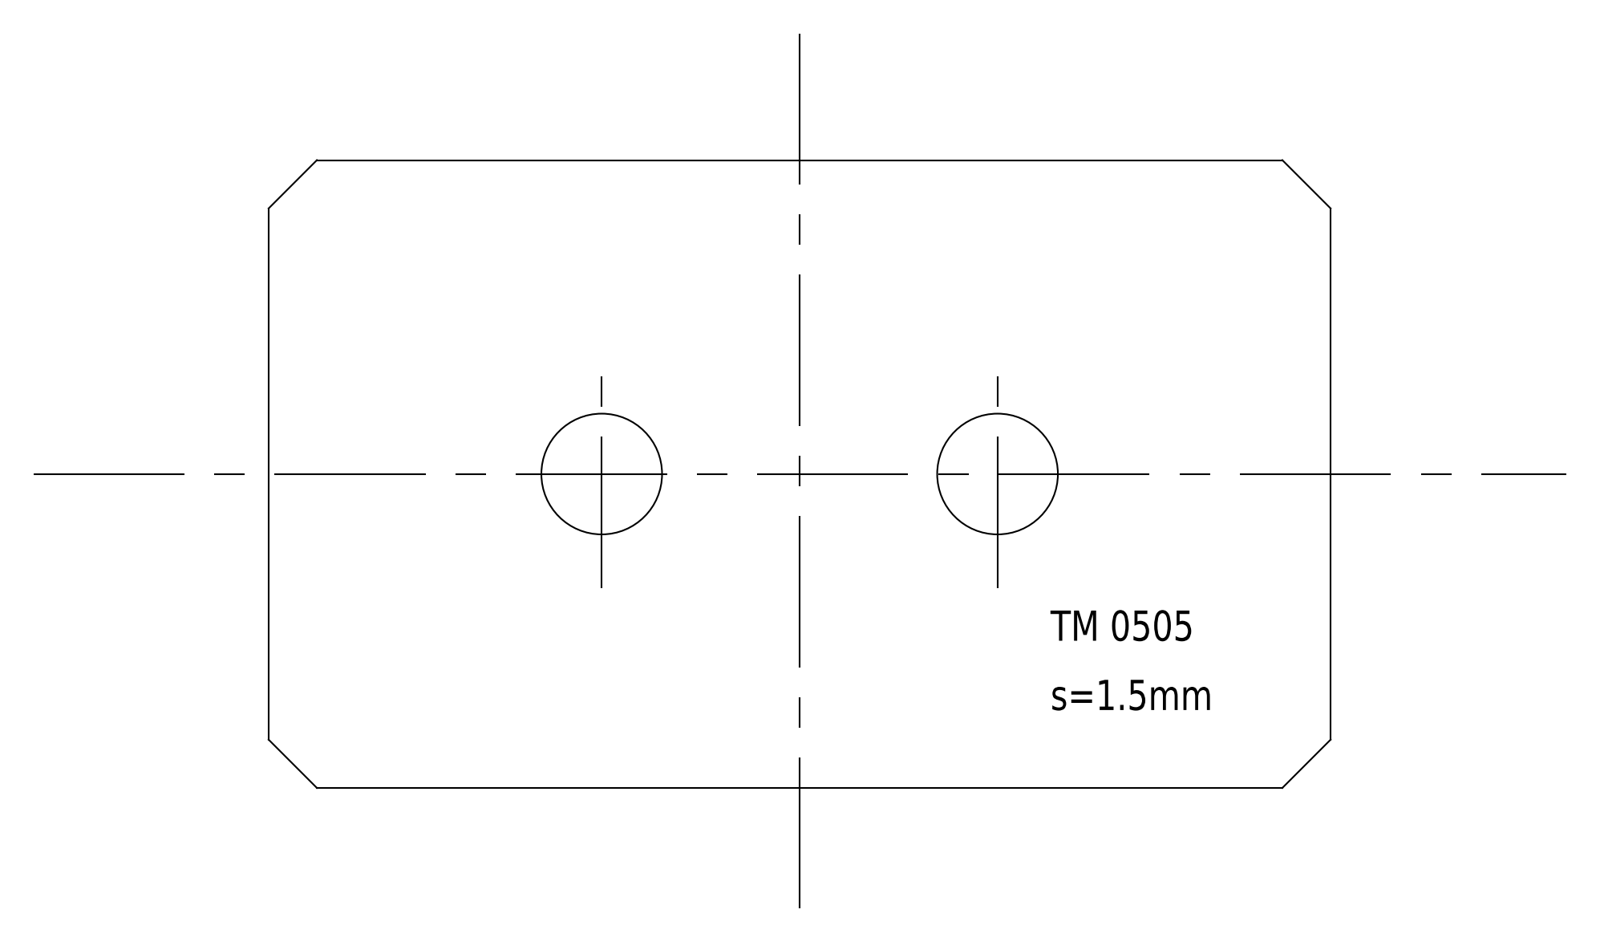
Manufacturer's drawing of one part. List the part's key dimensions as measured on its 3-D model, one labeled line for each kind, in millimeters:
Part name (STEP PRODUCT): TM 0505
STEP written by: SolidWorks 2009 (AUTOMOTIVE_DESIGN)
Units: millimetres
Bodies: 1 solid, 14 faces (10 planar, 4 cylindrical, 0 other)
Overall size (bounding box): 44 × 26 × 1.5
Volume: 1 645 mm³ · Surface area: 2 444 mm²
Round holes (diameter × count): ⌀5 ×2
Main face-to-face distances: 1.5, 26, 44, 46.66
Hole centre spacings: 16.4
